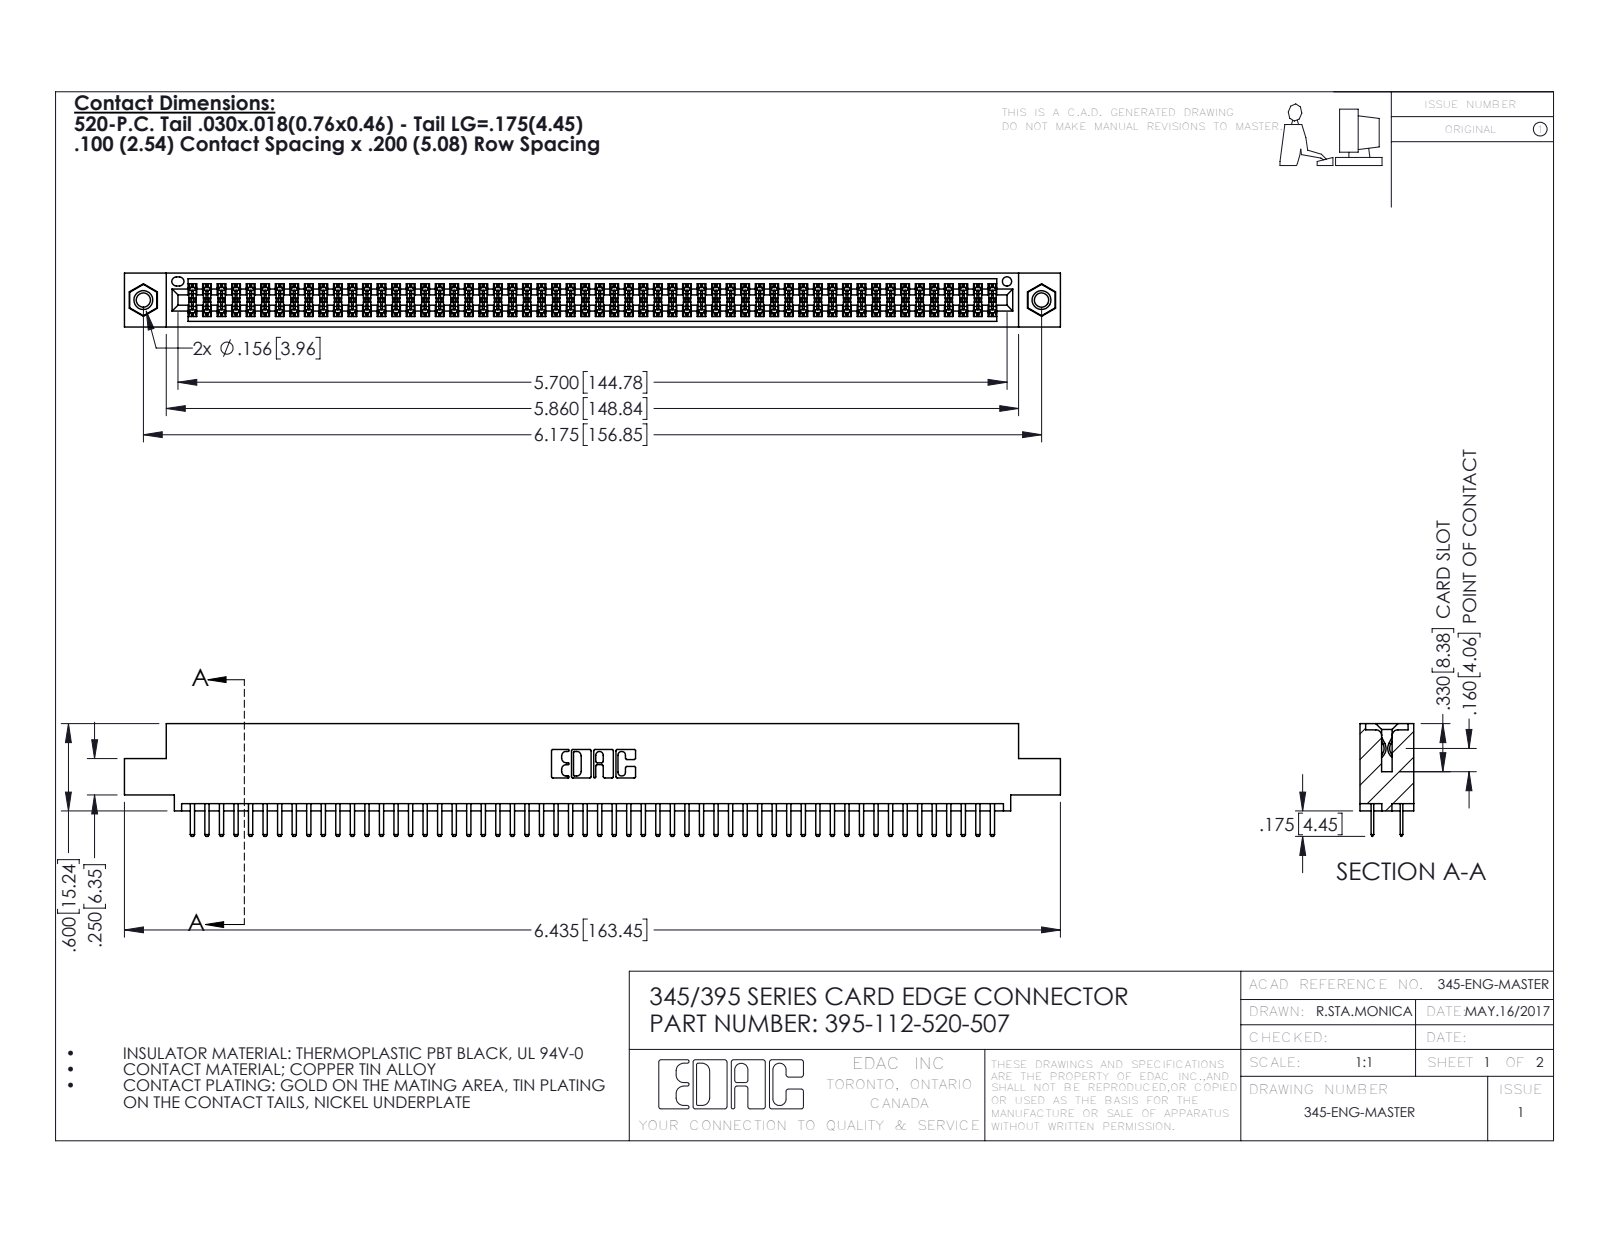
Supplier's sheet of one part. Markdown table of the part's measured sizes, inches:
| quantity | value |
| --- | --- |
| part name | 345 Part_0.110 Offset - 0.156 Dia-TI; 345-250-001_345-250-005-103; 345-292-001_345-293-120; 395-112-520-507 |
| STEP written by | SolidWorks 2016 (CONFIG_CONTROL_DESIGN) |
| units | inches |
| bodies | 115 solids, 6238 faces (4036 planar, 2186 cylindrical, 16 other) |
| overall size | 6.435 × 0.775 × 0.37 |
| volume | 0.969 in³ |
| surface area | 36.81 in² |
| round holes (diameter × count) | 0.098 × 2, 0.125 × 2, 0.156 × 2, 0.064 × 1 |
| round bosses / shafts (diameter × count) | 0.155 × 2 |
| partial cylindrical surfaces (radius × count) | 0.006 × 168, 0.01 × 116, 0.01 × 22, 0.007 × 6, 0.031 × 6, 0.026 × 3, 0.014 × 2, 0.019 × 2 |
| main face-to-face distances | 0.072, 0.298, 0.2, 0.37, 0.098, 0.272, 0.025, 0.225, 0.022, 0.072 |
| hole center spacings | 0.27, 5.939, 6.175 |
